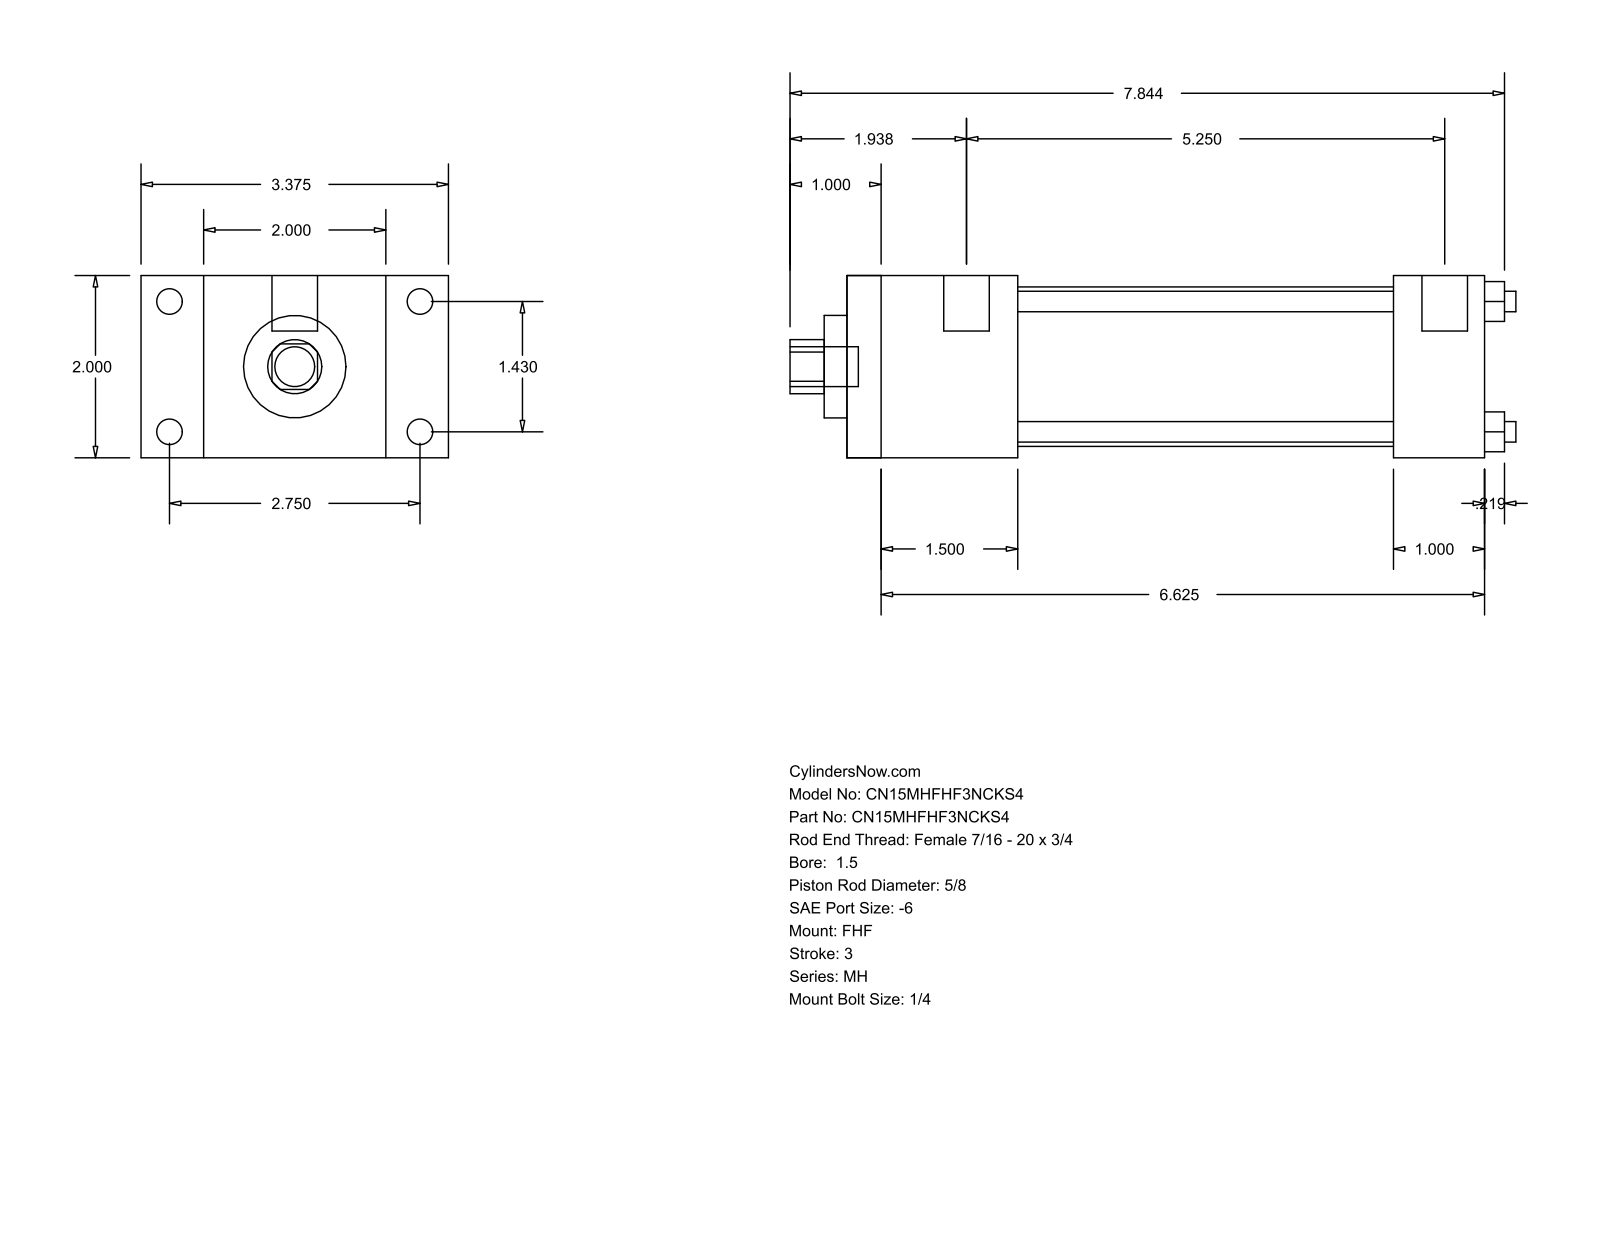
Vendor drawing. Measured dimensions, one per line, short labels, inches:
name: MH_FHF__0150_0.625
written by: GSSL Pune (CONFIG_CONTROL_DESIGN)
unit: in
bodies: 0 solids, 88 faces (60 planar, 28 cylindrical, 0 other)
size: 7.969 × 3.375 × 2
holes: 4× ⌀0.225, 1× ⌀0.625, 1× ⌀1.125, 1× ⌀1.75
bosses: 4× ⌀0.281, 4× ⌀0.219, 2× ⌀0.5, 1× ⌀0.437
rounds: 1× R0.297
face distances: 2, 0.687, 2.687, 1.875, 3.375, 7, 5.125, 6, 4.125, 1
hole spacings: 1.011, 1.43, 2.022
